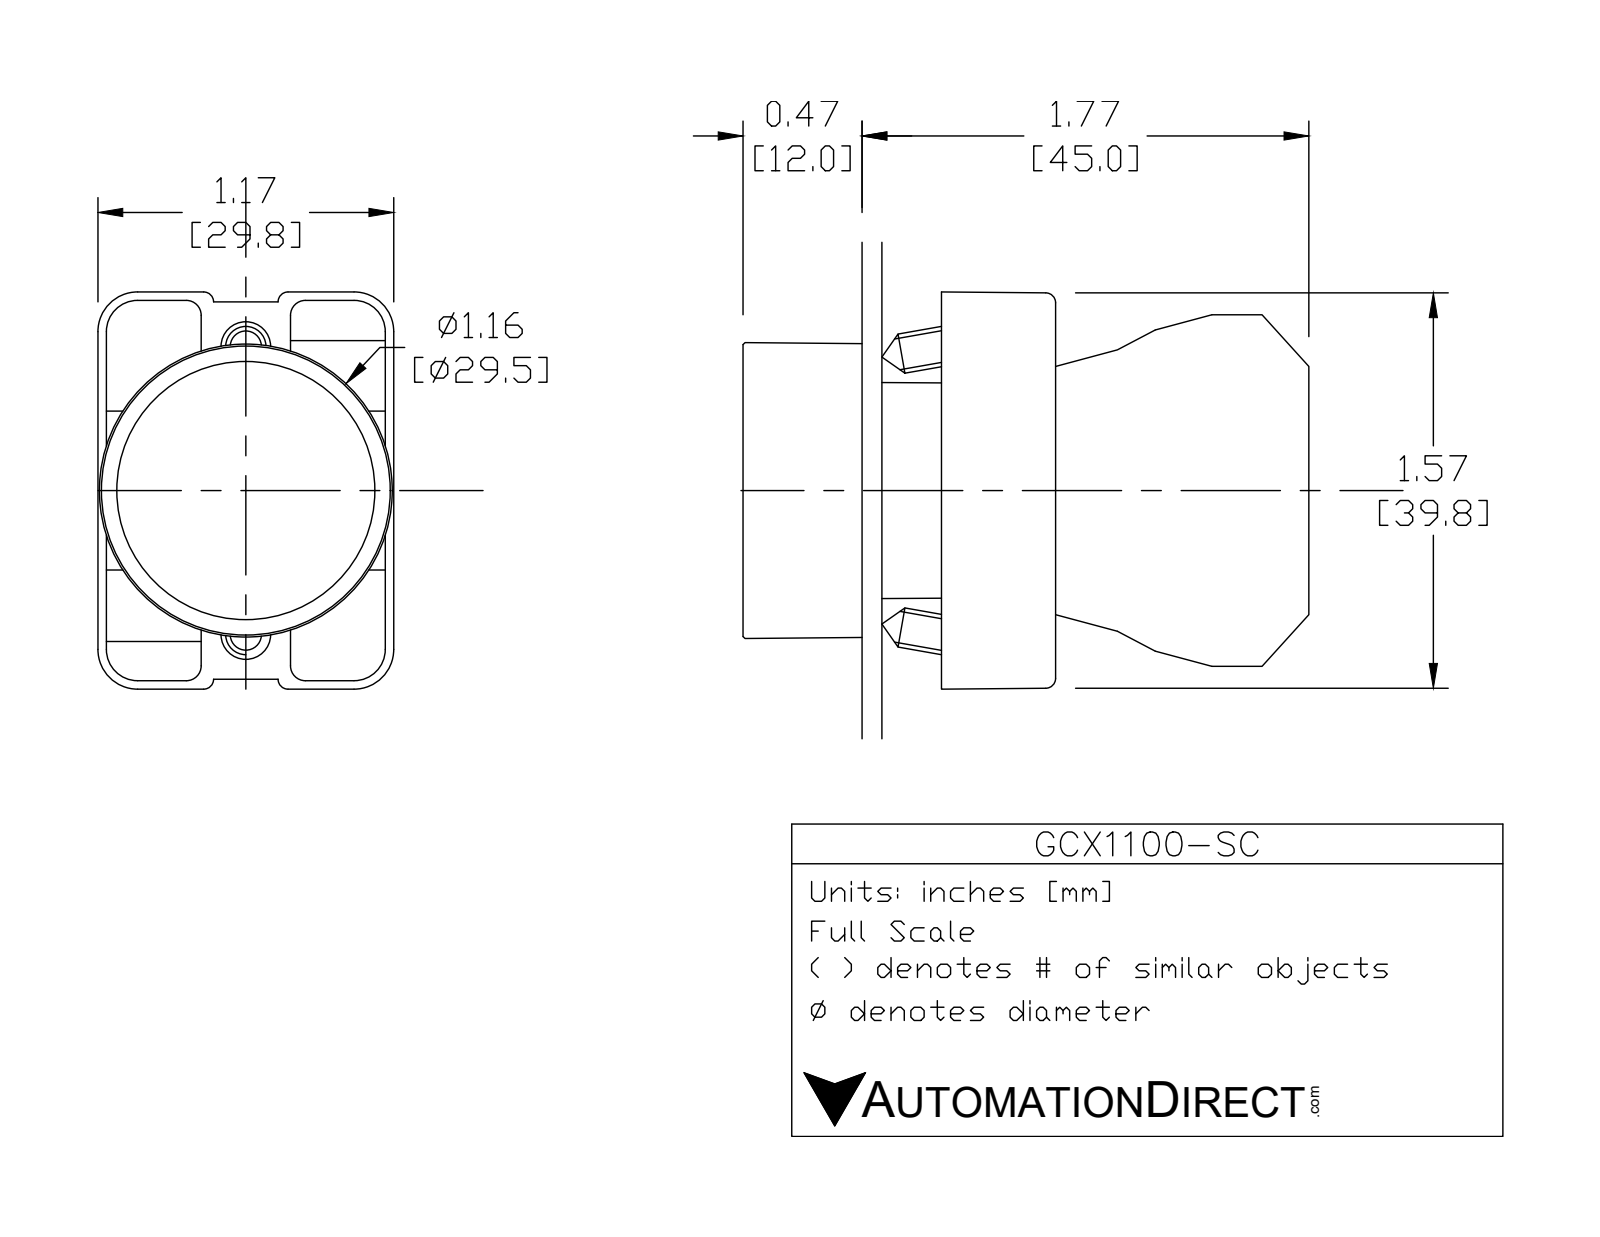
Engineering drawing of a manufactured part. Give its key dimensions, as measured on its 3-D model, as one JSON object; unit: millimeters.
{"part_name": "GCX1100-SC; ecx1029; GCX1100 OPERATOR", "step_written_by": "SolidWorks 2016 (AUTOMOTIVE_DESIGN)", "units": "millimeters", "bodies": {"solids": 5, "faces": 288, "planar": 147, "cylindrical": 118, "other": 23}, "overall_size": [40.2, 35.7, 29.9], "volume_mm3": 17860, "surface_area_mm2": 13170, "round_holes": [[3.1, 2], [3.3, 2], [5, 1], [22.3, 1], [22.6, 1], [26, 1]], "round_bosses_or_shafts": [[4, 2], [29.8, 1], [25.5, 1], [24, 1], [21.7, 1], [19.8, 1]], "partial_cylinders_radius": [[1.5, 24], [1, 12], [3.1, 12], [4, 12], [1, 4], [3.3, 2], [10, 1], [10.1, 1]], "face_to_face_distances": [0.8, 18.3, 30.3, 12, 0.8, 17.5, 29.5, 3.1, 2.3, 15.2]}
